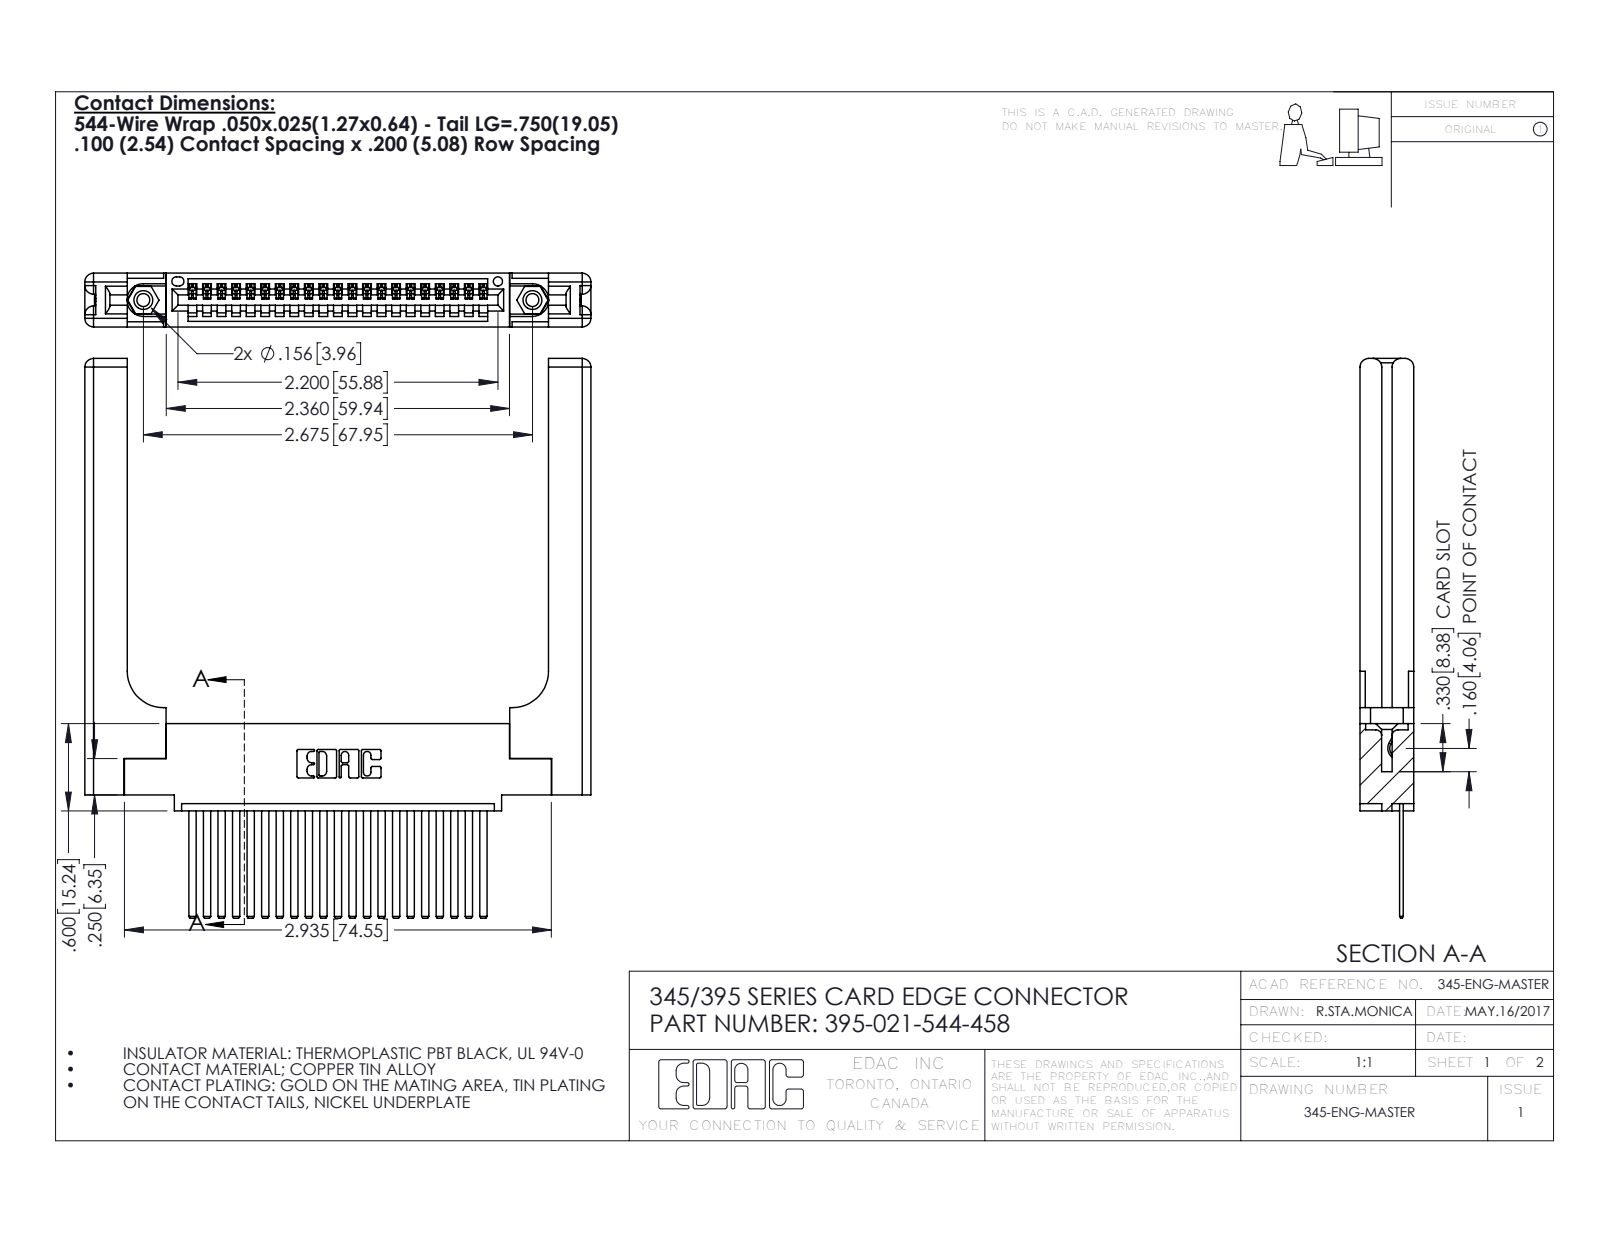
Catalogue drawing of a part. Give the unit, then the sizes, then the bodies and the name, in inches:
Units: inches
Overall size (bounding box): 3.847 × 3.479 × 0.37
Round holes (diameter × count): ⌀0.089 ×2, ⌀0.125 ×2, ⌀0.156 ×2, ⌀0.064 ×1
Round bosses / shafts (diameter × count): ⌀0.155 ×2
Partial cylindrical surfaces — rounded edges, fillets, slot ends (radius × count): R0.006 ×42, R0.01 ×22, R0.06 ×16, R0.007 ×6, R0.031 ×6, R0.026 ×3, R0.03 ×2, R0.031 ×2
Main face-to-face distances: 0.37, 0.072, 0.298, 0.098, 0.272, 0.025, 0.148, 0.15, 0.077, 0.22
Hole centre spacings: 0.27, 2.441, 2.675
Volume: 1.031 in³ · Surface area: 26.32 in²
Bodies: 26 solids, 1478 faces (988 planar, 430 cylindrical, 60 other)
Part name (STEP PRODUCT): 345 Part_0.110 Offset - 0.156 Dia-TH; 345-220-058_345-220-058; 345-292-001_345-293-144; 395-021-544-458 (+1 more)
STEP written by: SolidWorks 2016 (CONFIG_CONTROL_DESIGN)
